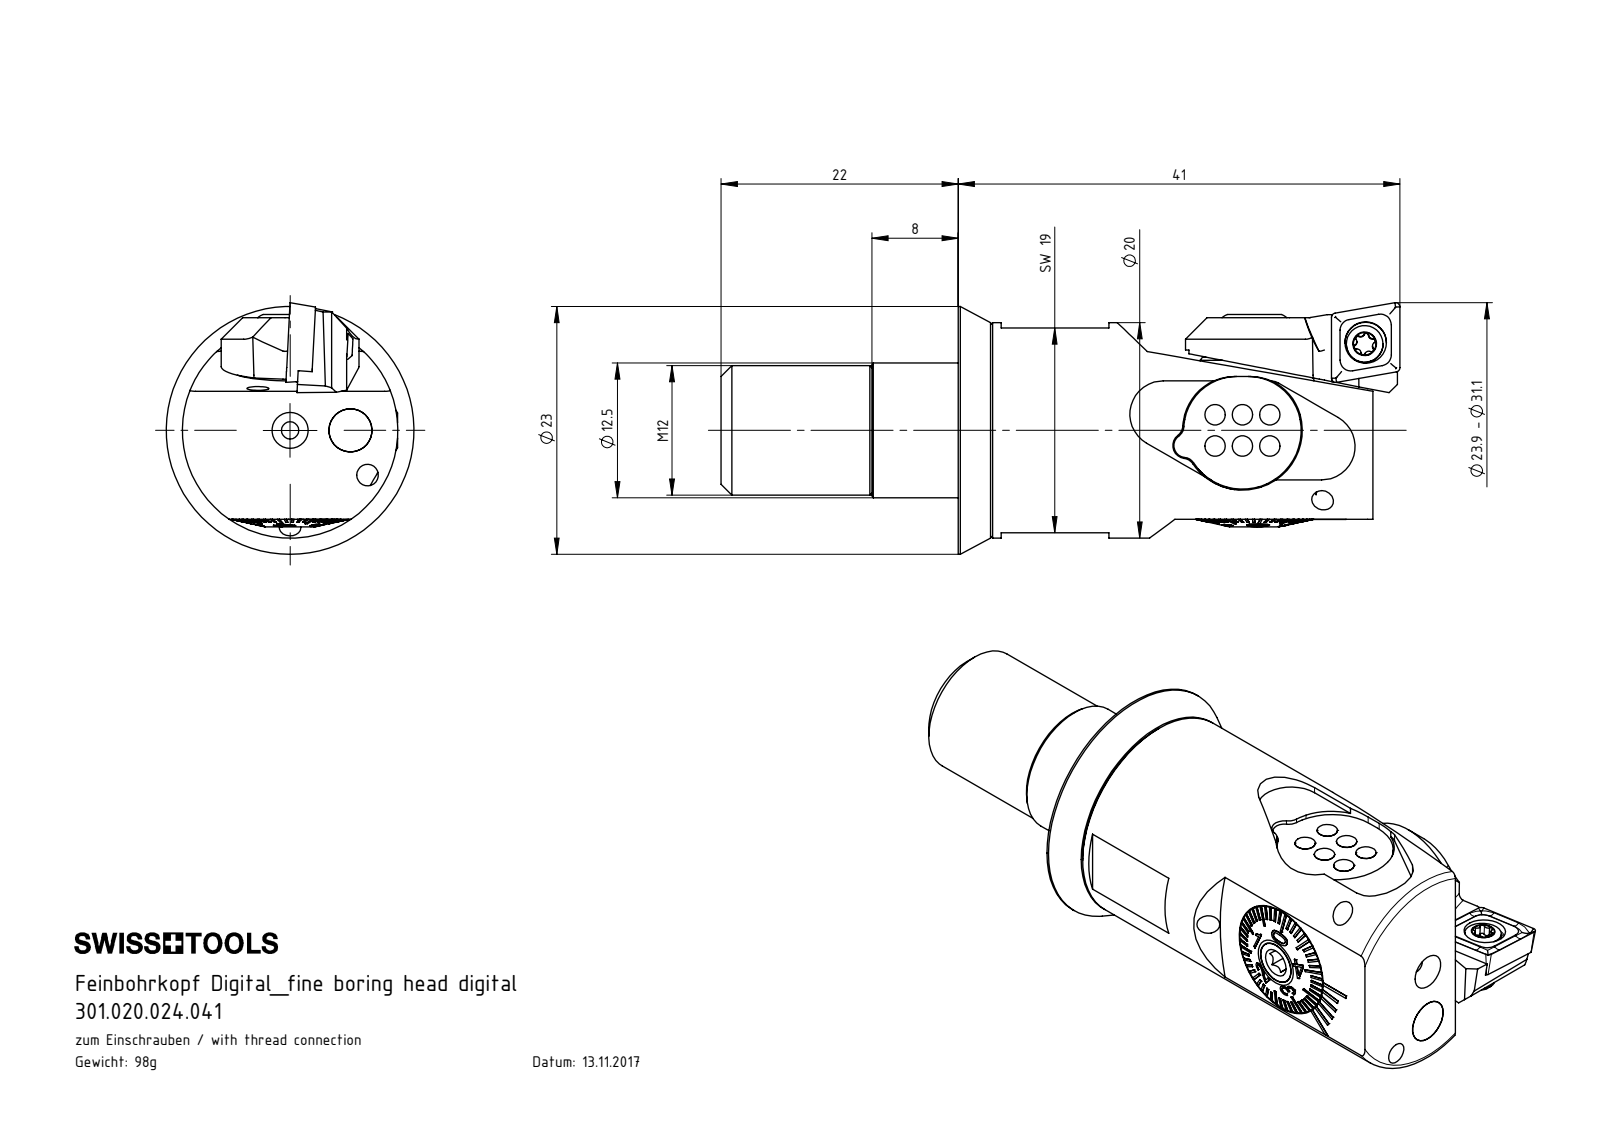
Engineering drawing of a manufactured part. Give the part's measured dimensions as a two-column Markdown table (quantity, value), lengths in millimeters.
| quantity | value |
| --- | --- |
| part name | HP4-ER2.008.028_A; F20-BG3.004.017_A; WCA-ER2.001.006_A; D23-D20.HP4.003_A (+8 more) |
| STEP written by | SolidWorks 2017 (CONFIG_CONTROL_DESIGN) |
| units | millimeters |
| bodies | 18 solids, 883 faces (387 planar, 193 cylindrical, 303 other) |
| overall size | 63 × 23.35 × 23 |
| volume | 12 613 mm³ |
| surface area | 10 313 mm² |
| round holes (diameter × count) | 2 × 5, 3.3 × 3, 0.7 × 1, 1.6 × 1, 1.9 × 1, 2.05 × 1, 2.4 × 1, 2.5 × 1, 2.8 × 1, 3 × 1, 3.85 × 1, 4 × 1 |
| round bosses / shafts (diameter × count) | 1.9 × 6, 6 × 2, 4 × 2, 3.95 × 2, 23 × 1, 20 × 1, 12 × 1, 10.98 × 1 |
| partial cylindrical surfaces (radius × count) | 0.21 × 6, 0.36 × 5, 1.1 × 3, 1.2 × 3, 5 × 3, 0.3 × 2, 0.5 × 2, 2 × 2 |
| main face-to-face distances | 3, 38.5, 35.5, 15.05, 8, 1.5, 11, 46.5, 6, 2.8 |
| hole center spacings | 1.14, 2.6, 3.51, 4.44, 5.6, 8.3 |
